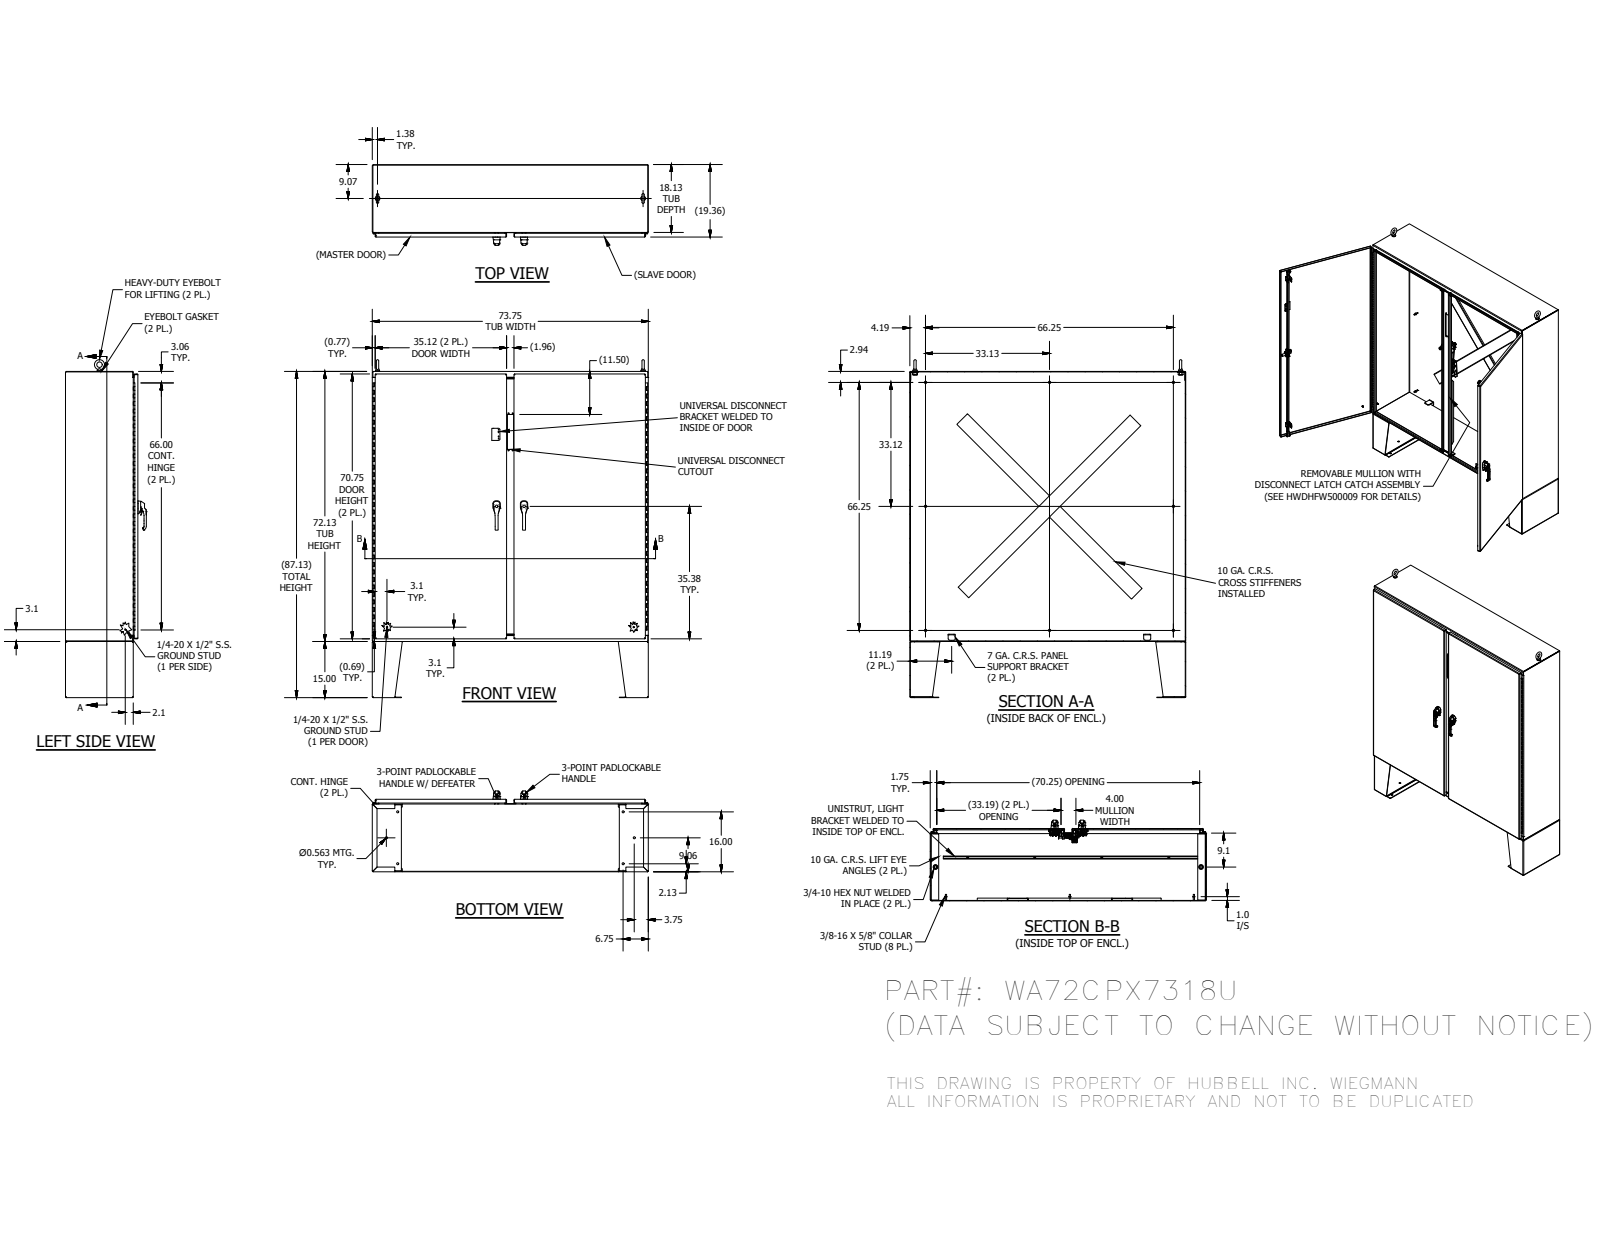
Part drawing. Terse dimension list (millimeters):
name: WA72CPX7318UBLS; WACPX7318UTOP; WACPX7318UBTM; 30364 (+8 more)
written by: Autodesk Inventor 2016 (AUTOMOTIVE_DESIGN)
unit: mm
bodies: 211 solids, 8671 faces (4059 planar, 2895 cylindrical, 1717 other)
size: 2292.29 × 1873.25 × 548.85
volume: 43 660 000 mm³; area: 26 620 000 mm²
holes: 21× ⌀6.35, 18× ⌀9.52, 18× ⌀14.29, 8× ⌀5.08, 8× ⌀5.16, 8× ⌀7.02, 8× ⌀7.94, 6× ⌀3.96, 6× ⌀4.83, 6× ⌀4.98, 6× ⌀5.11, 6× ⌀5.4
bosses: 17× ⌀6.35, 16× ⌀8.38, 14× ⌀15.88, 9× ⌀14.29, 9× ⌀9.52, 9× ⌀8.56, 8× ⌀25.4, 8× ⌀11.13
rounds: 343× R0.5, 202× R0.3, 144× R0.51, 44× R0.47, 43× R2.38, 40× R1.27, 40× R3.17, 27× R2
face distances: 3.4, 488.1, 3.41, 484.7, 491.5, 1828.57, 1873.25, 3.18, 1869.84, 1825.16
hole spacings: 186.28, 27.99, 187.63, 70.08, 22.5, 29, 32.29, 40.66
